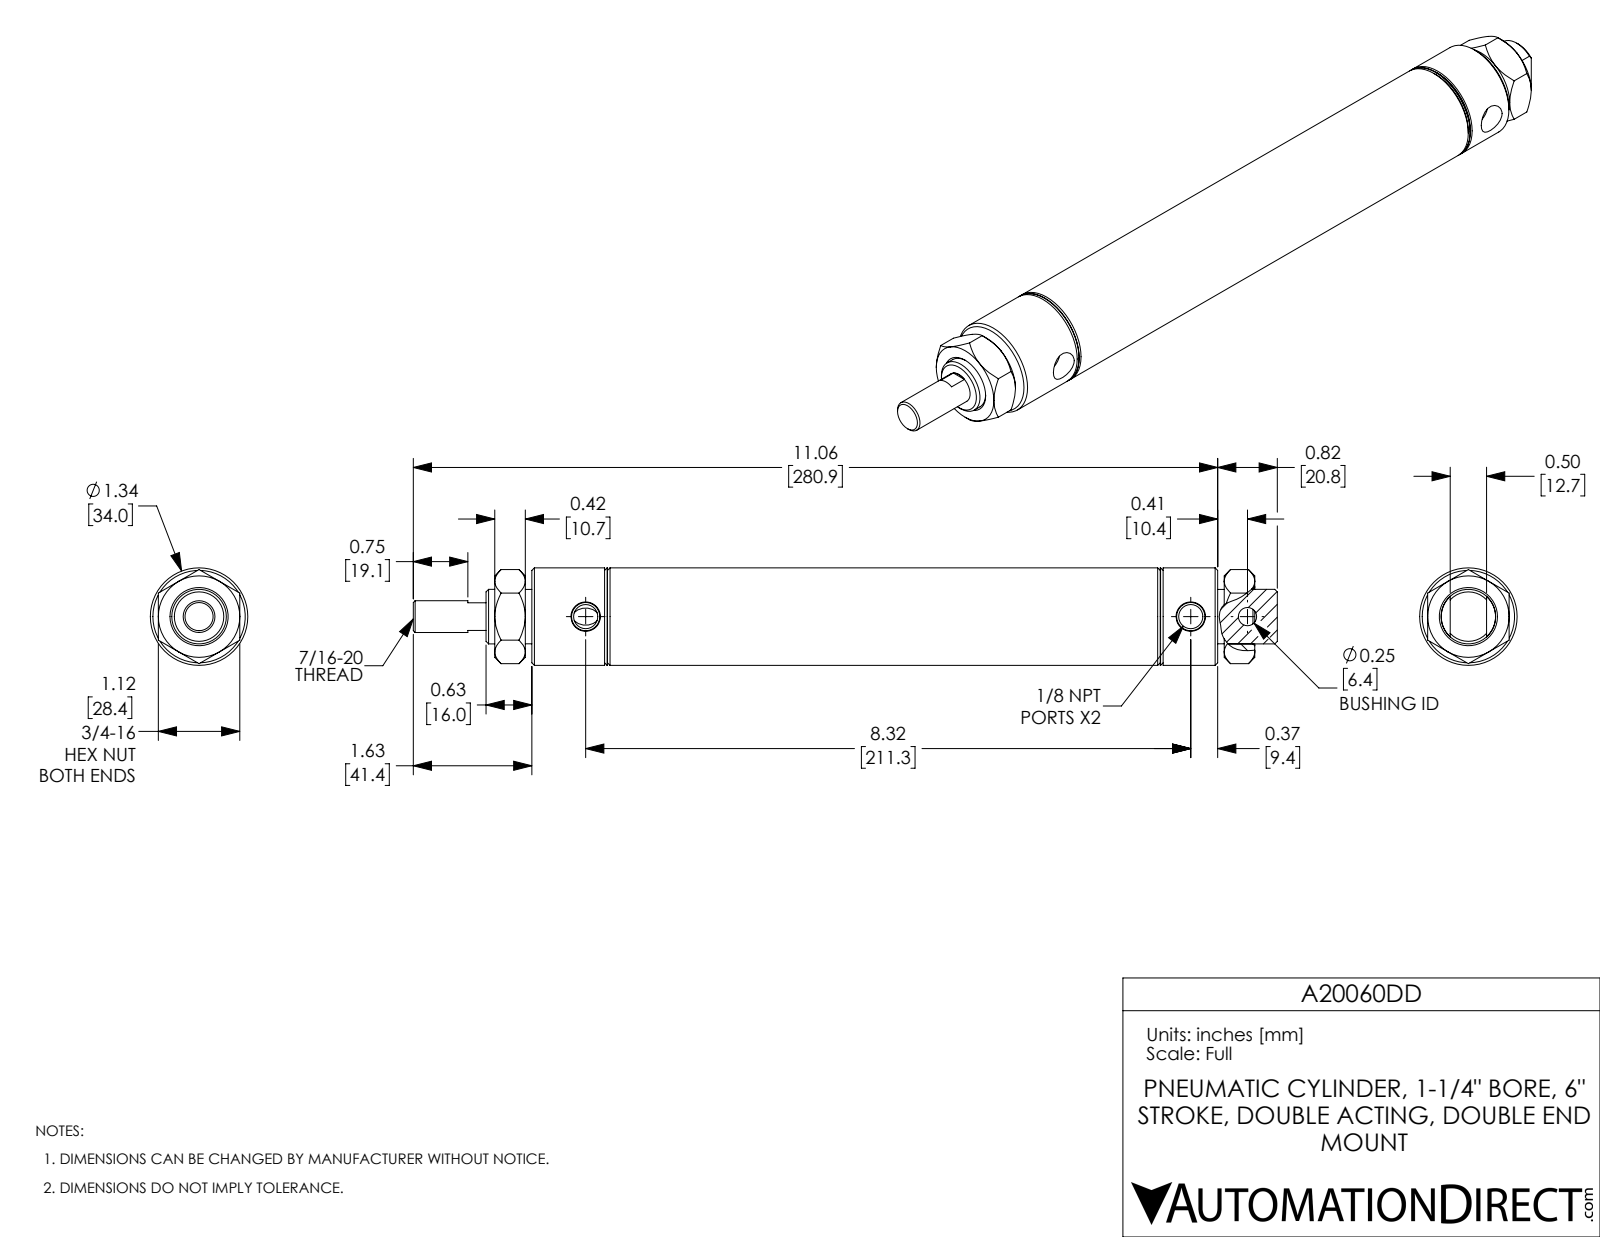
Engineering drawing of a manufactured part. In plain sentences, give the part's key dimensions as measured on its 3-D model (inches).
The part is named "A20060DD; A20060DD_Mounting Nut_D-3556; A20060DD-Rod; A20060DD-MainBody". Its 3-D file was written by "SolidWorks 2017 (AUTOMOTIVE_DESIGN)". It is 4 solids with 138 faces: 44 planar, 36 cylindrical and 58 other. Overall it measures 11.88 by 1.34 by 1.34 inches. Its volume is 7.938 cubic inches and its surface area 102.4 square inches. Round holes: 2 of diameter 0.332, 1 of diameter 0.251, 1 of diameter 0.437, 1 of diameter 0.75, 1 of diameter 1.25. Round bosses or shafts: 1 of diameter 1.34, 1 of diameter 0.747. The main face-to-face distances are 1.465, 7.965, 0.5, 1.12, 6.5, 6, 0.31, 0.42, 10.03, 1.965. The hole center spacings are 0.78, 8.32, 9.1.
